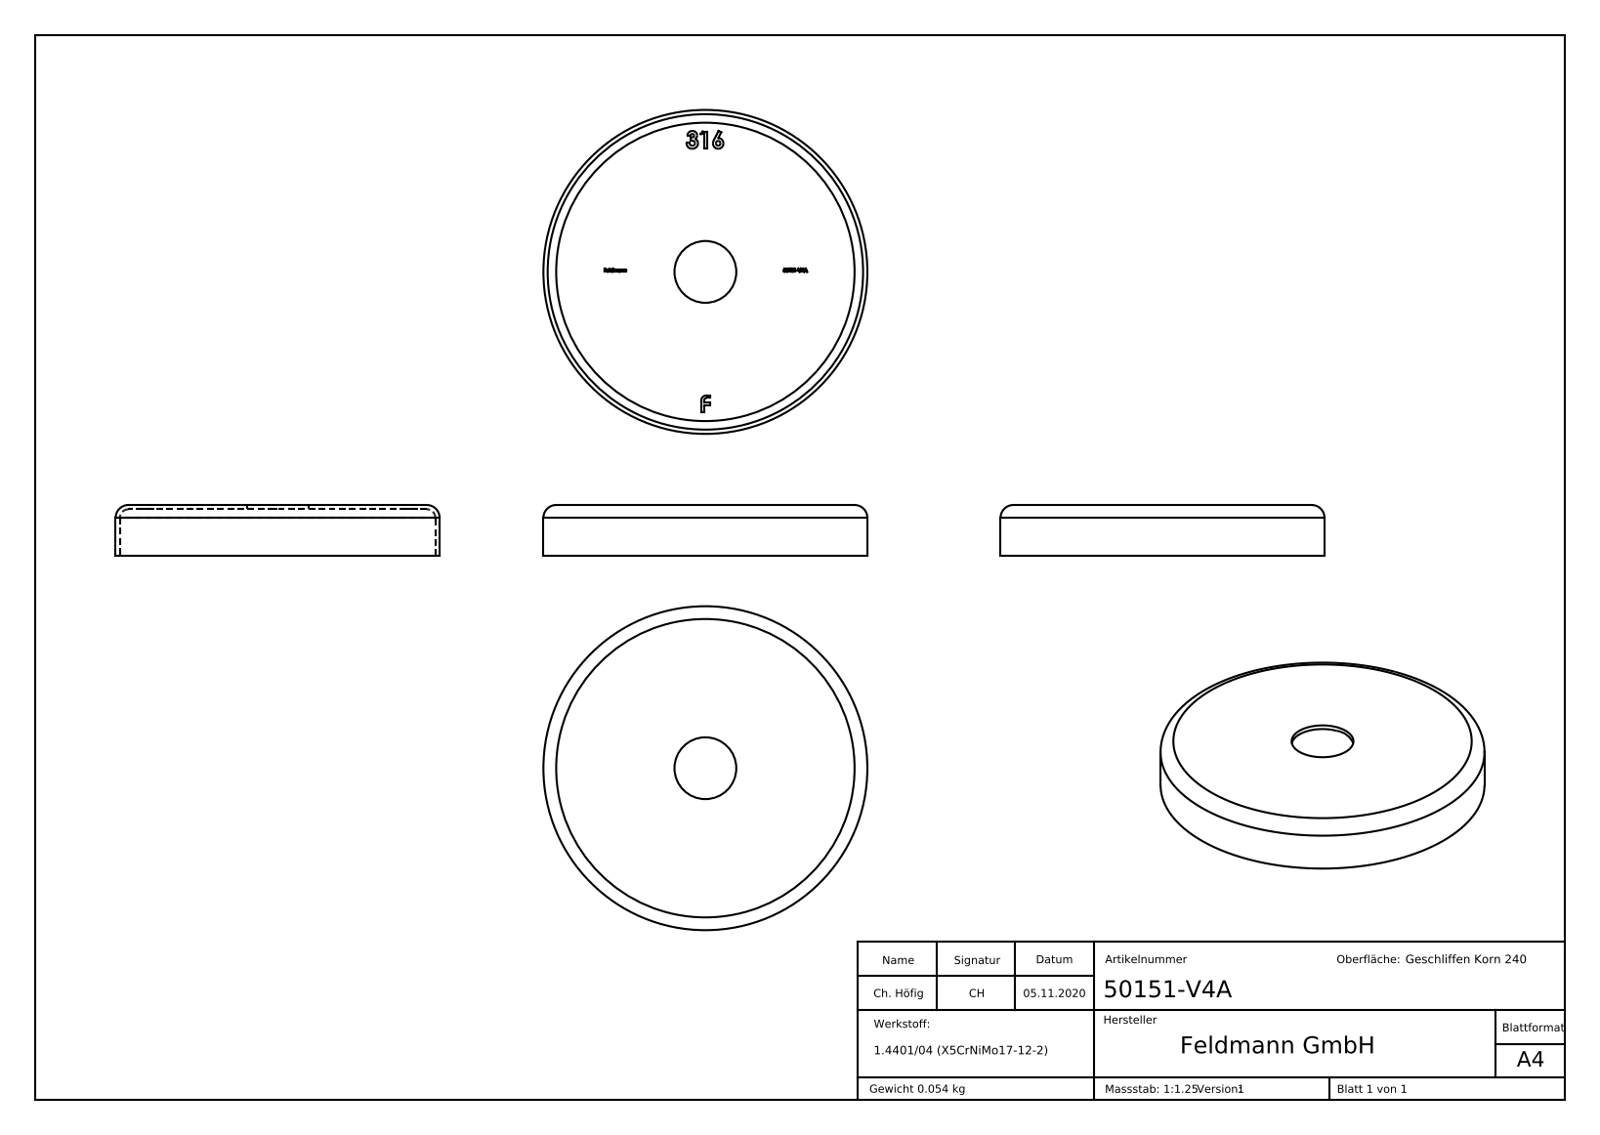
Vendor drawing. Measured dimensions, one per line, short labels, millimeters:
name: 50151-V4A
written by: SolidWorks 2018 (CONFIG_CONTROL_DESIGN)
unit: mm
bodies: 1 solid, 272 faces (166 planar, 6 cylindrical, 100 other)
size: 76 × 76 × 12
volume: 6 705 mm³; area: 13 709 mm²
holes: 1× ⌀14.5, 1× ⌀74
bosses: 1× ⌀76
face distances: 1, 11, 12, 11.1, 0.9, 0.71, 0.75, 0.73, 1.44, 31.52
